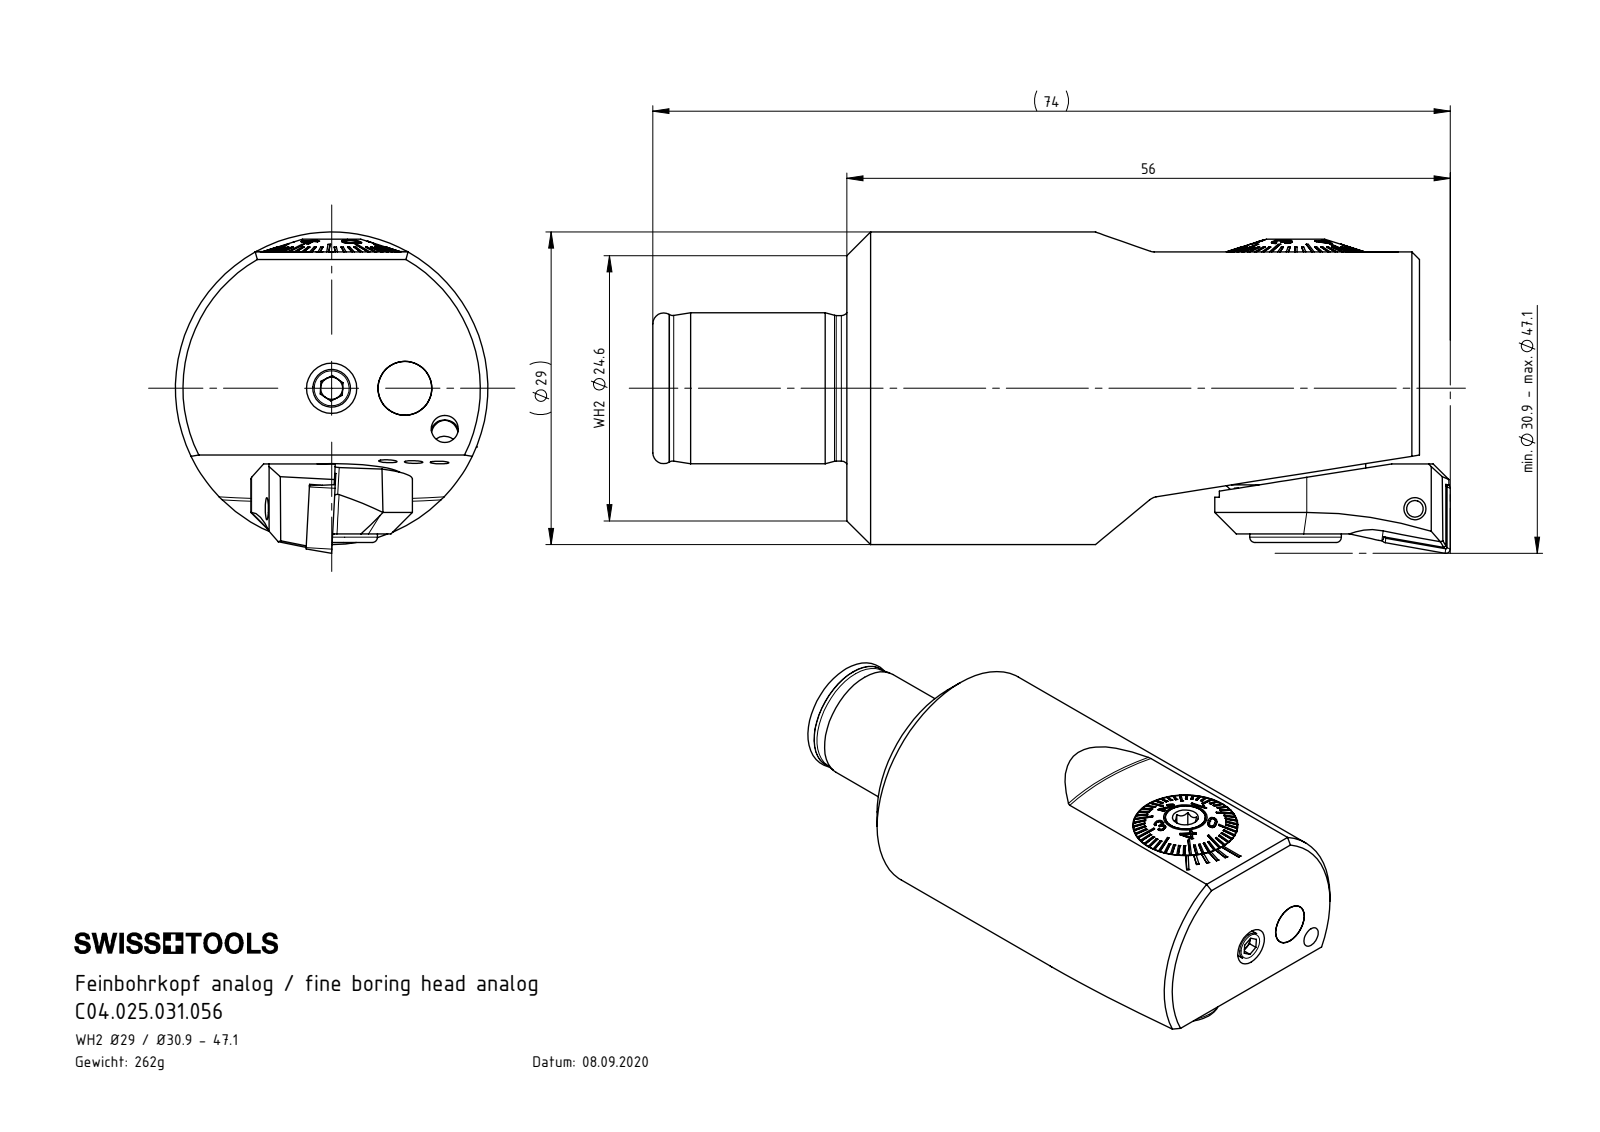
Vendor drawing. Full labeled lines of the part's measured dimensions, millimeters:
Part name (STEP PRODUCT): F25-BG1.009.006_A; Fxx-MAB.xxx.xxx_A_F25-DA3; F25-BG1.DA3.013_A_Aktuell 06.2014-M1x2; F25-BG2.008.009_A (+8 more)
STEP written by: SolidWorks 2017 (CONFIG_CONTROL_DESIGN)
Units: millimetres
Bodies: 14 solids, 671 faces (310 planar, 109 cylindrical, 252 other)
Overall size (bounding box): 71.15 × 29 × 29
Volume: 32 992 mm³ · Surface area: 12 801 mm²
Round holes (diameter × count): ⌀1.5 ×3, ⌀2.5 ×2, ⌀4.2 ×2, ⌀5 ×2, ⌀2.05 ×1, ⌀2.4 ×1, ⌀2.7 ×1, ⌀3 ×1, ⌀3.3 ×1, ⌀5.5 ×1, ⌀6.4 ×1, ⌀7.3 ×1
Round bosses / shafts (diameter × count): ⌀5 ×2, ⌀4.95 ×2, ⌀29 ×1, ⌀14 ×1, ⌀13.5 ×1, ⌀13 ×1, ⌀12.98 ×1, ⌀12.85 ×1
Partial cylindrical surfaces — rounded edges, fillets, slot ends (radius × count): R1.4 ×4, R0.5 ×2, R1.5 ×2, R0.2 ×1, R1.25 ×1, R2 ×1
Main face-to-face distances: 53.15, 18, 1.5, 3.91, 3.1, 0.81, 1.6, 2.31, 71.15, 19.6
Hole centre spacings: 6.8, 7.32
